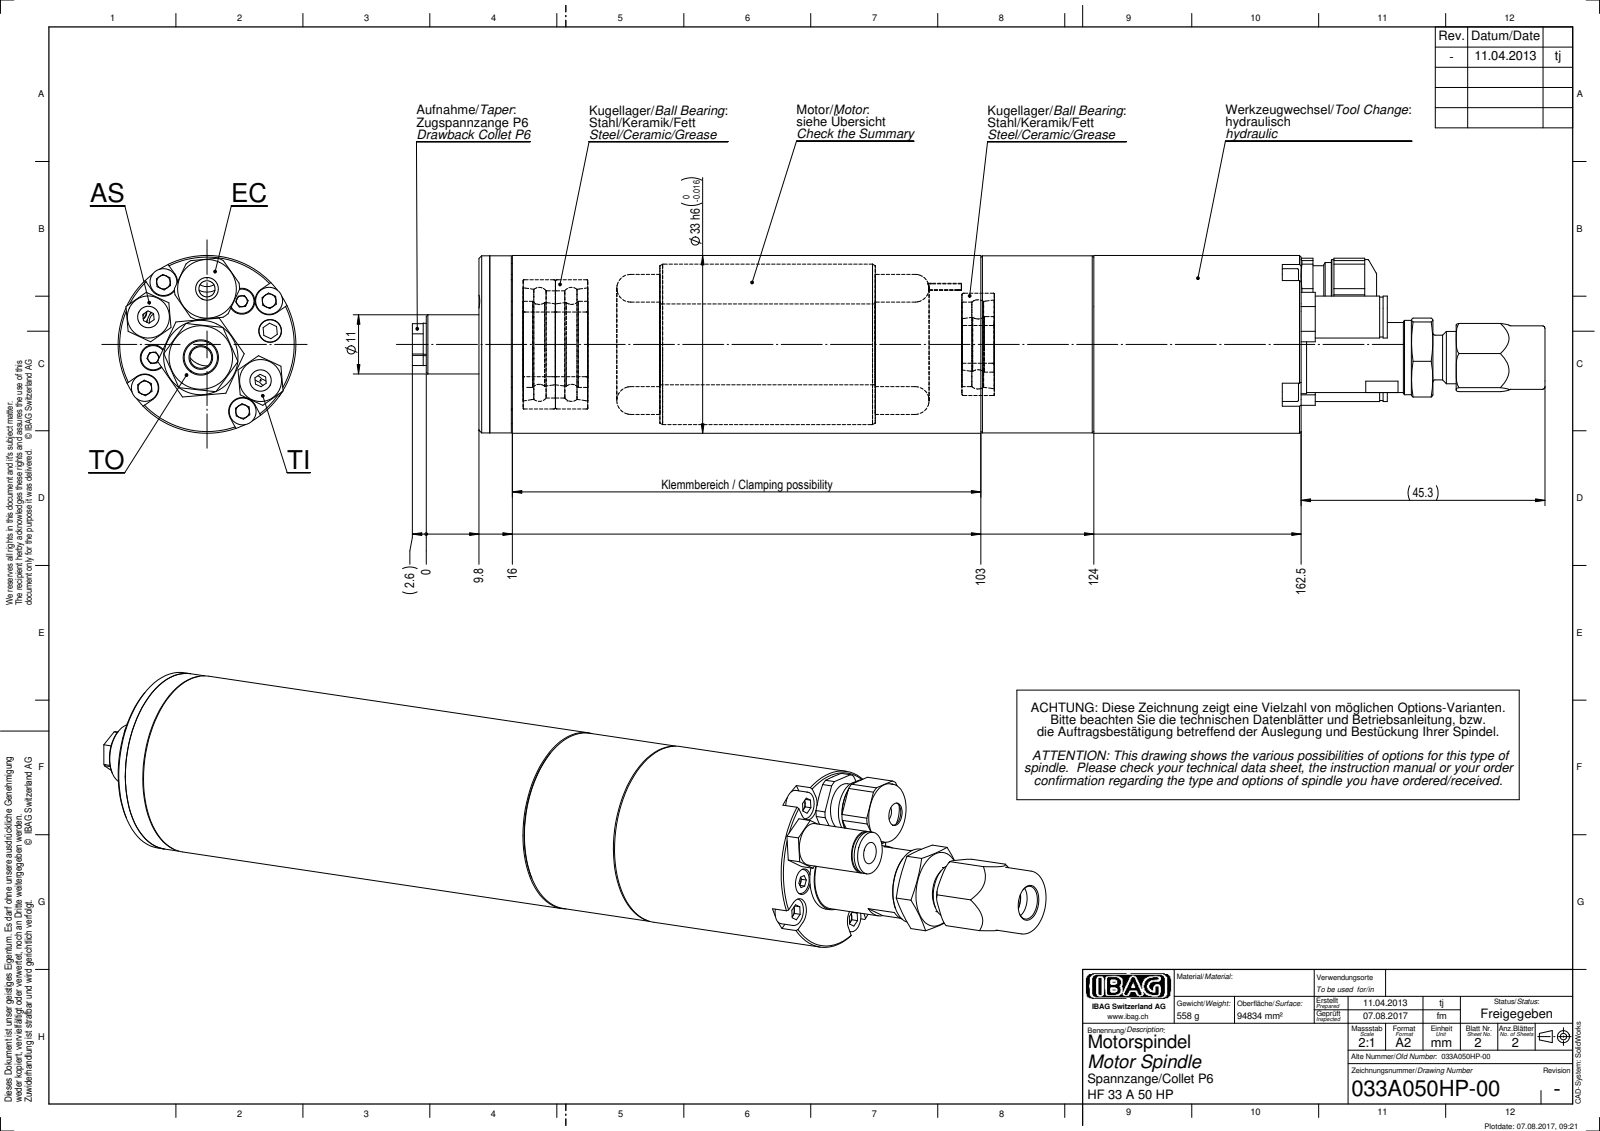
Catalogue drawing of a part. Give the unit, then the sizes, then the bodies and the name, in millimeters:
Units: millimetres
Overall size (bounding box): 210.36 × 33 × 33
Round holes (diameter × count): ⌀4 ×2, ⌀4.2 ×2, ⌀4.8 ×2, ⌀2 ×1, ⌀3 ×1, ⌀6.15 ×1, ⌀9.15 ×1, ⌀11.4 ×1
Round bosses / shafts (diameter × count): ⌀5 ×7, ⌀7.8 ×2, ⌀33 ×1, ⌀32.9 ×1, ⌀13.8 ×1, ⌀13.4 ×1, ⌀13 ×1, ⌀11.8 ×1
Partial cylindrical surfaces — rounded edges, fillets, slot ends (radius × count): R2.6 ×4, R0.76 ×3, R6.05 ×1
Main face-to-face distances: 152.7, 6.2, 146.5, 6, 146.7, 114.2, 108.2, 108, 38.5, 12
Hole centre spacings: 10.3, 12, 2.7, 6.88, 7.61, 7.62, 8.85, 9.37
Bodies: 0 solids, 380 faces (168 planar, 117 cylindrical, 95 other)
Part name (STEP PRODUCT): 033A050HP-00
STEP written by: SolidWorks 2012 (CONFIG_CONTROL_DESIGN)
